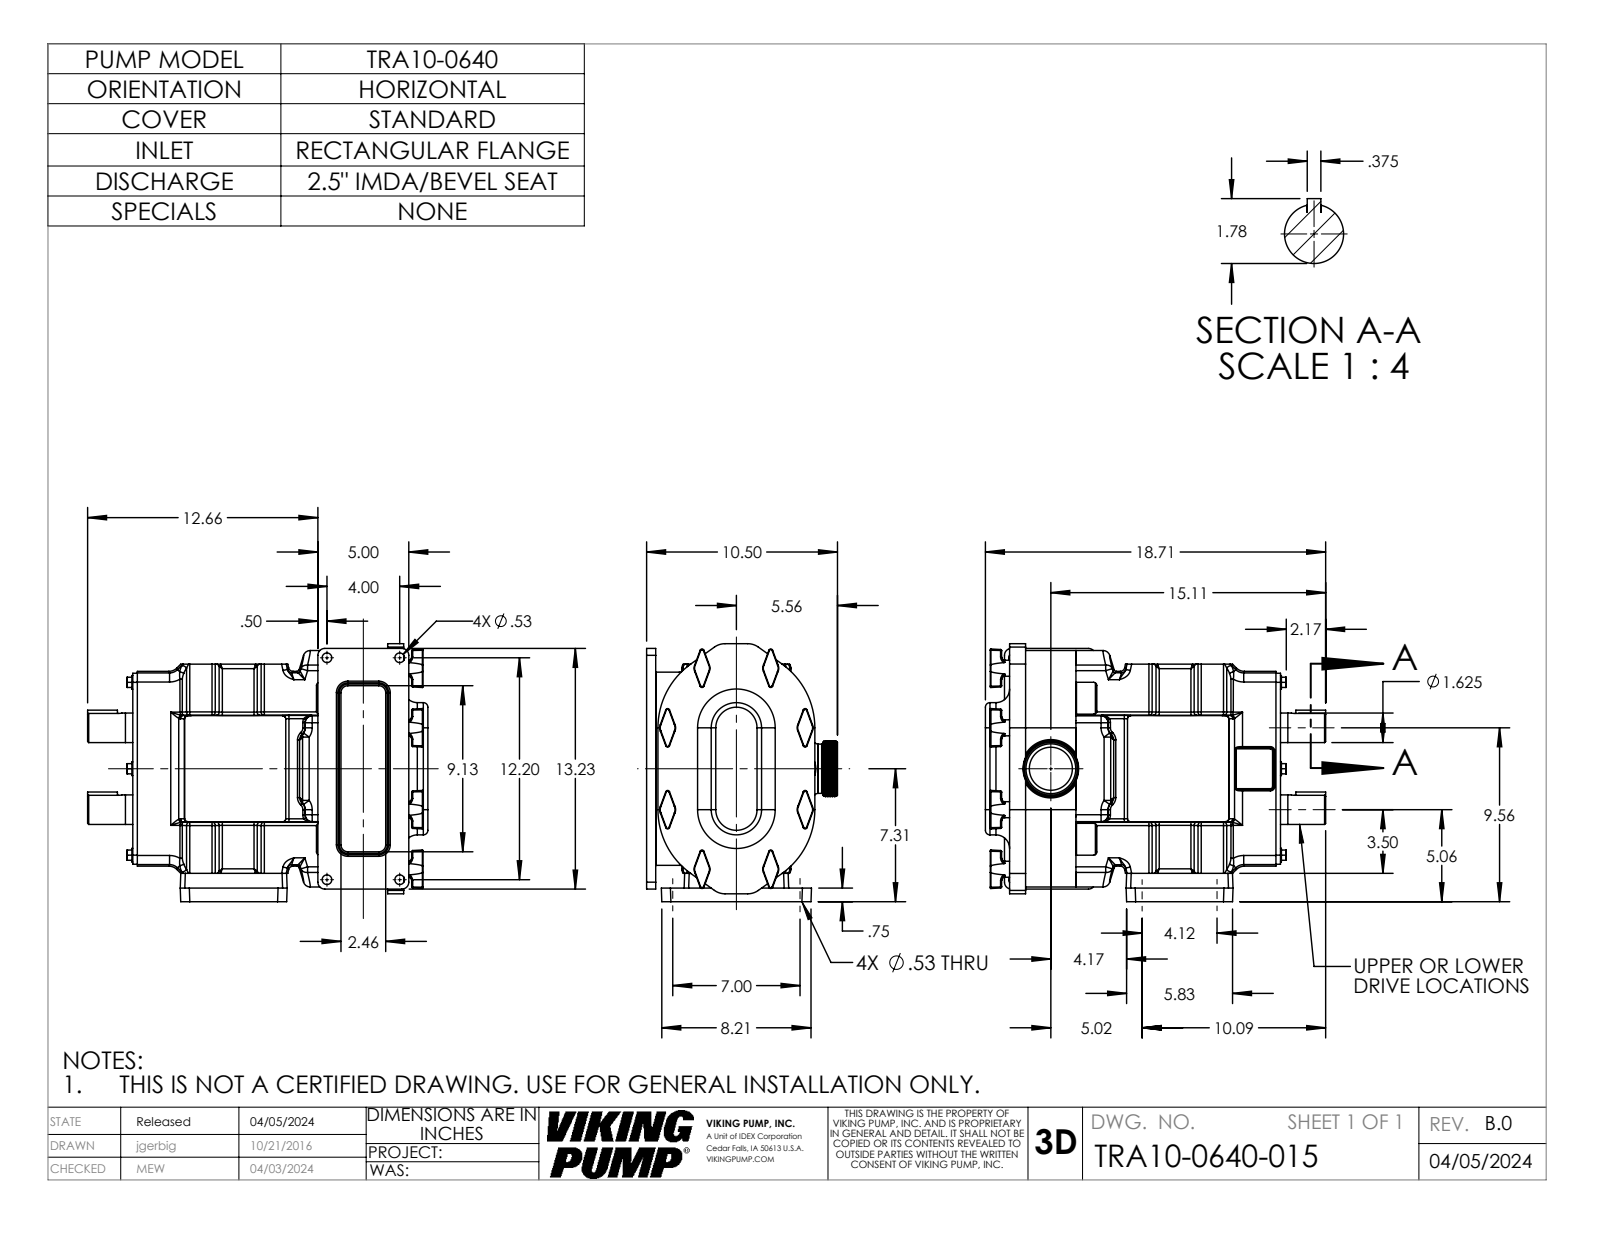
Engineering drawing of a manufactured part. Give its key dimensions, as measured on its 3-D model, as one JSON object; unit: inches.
{"part_name": "0600IMDA25; TRA10-0600-GEARBOX-H; TRA10-0640-BODY; TRA10-0600-COVER-STD (+1 more)", "step_written_by": "SolidWorks 2022 (AUTOMOTIVE_DESIGN)", "units": "inches", "bodies": {"solids": 4, "faces": 1116, "planar": 295, "cylindrical": 411, "other": 410}, "overall_size": [18.714, 14.185, 10.498], "volume_in3": 1229, "surface_area_in2": 1434, "round_holes": [[0.531, 8], [2.368, 1]], "round_bosses_or_shafts": [[0.88, 8], [0.75, 6], [1.624, 2], [3.056, 1], [2.909, 1], [2.708, 1]], "partial_cylinders_radius": [[0.18, 44], [0.06, 43], [0.03, 36], [0.38, 36], [0.25, 32], [0.12, 24], [0.5, 22], [0.09, 16]], "face_to_face_distances": [2.769, 0.5, 1.437, 0.88, 3.649, 7.937, 0.36, 11.25, 14.899, 14.019], "hole_center_spacings": [4, 4.12, 6.404, 6.435, 7, 8.122, 12.2, 12.839]}
